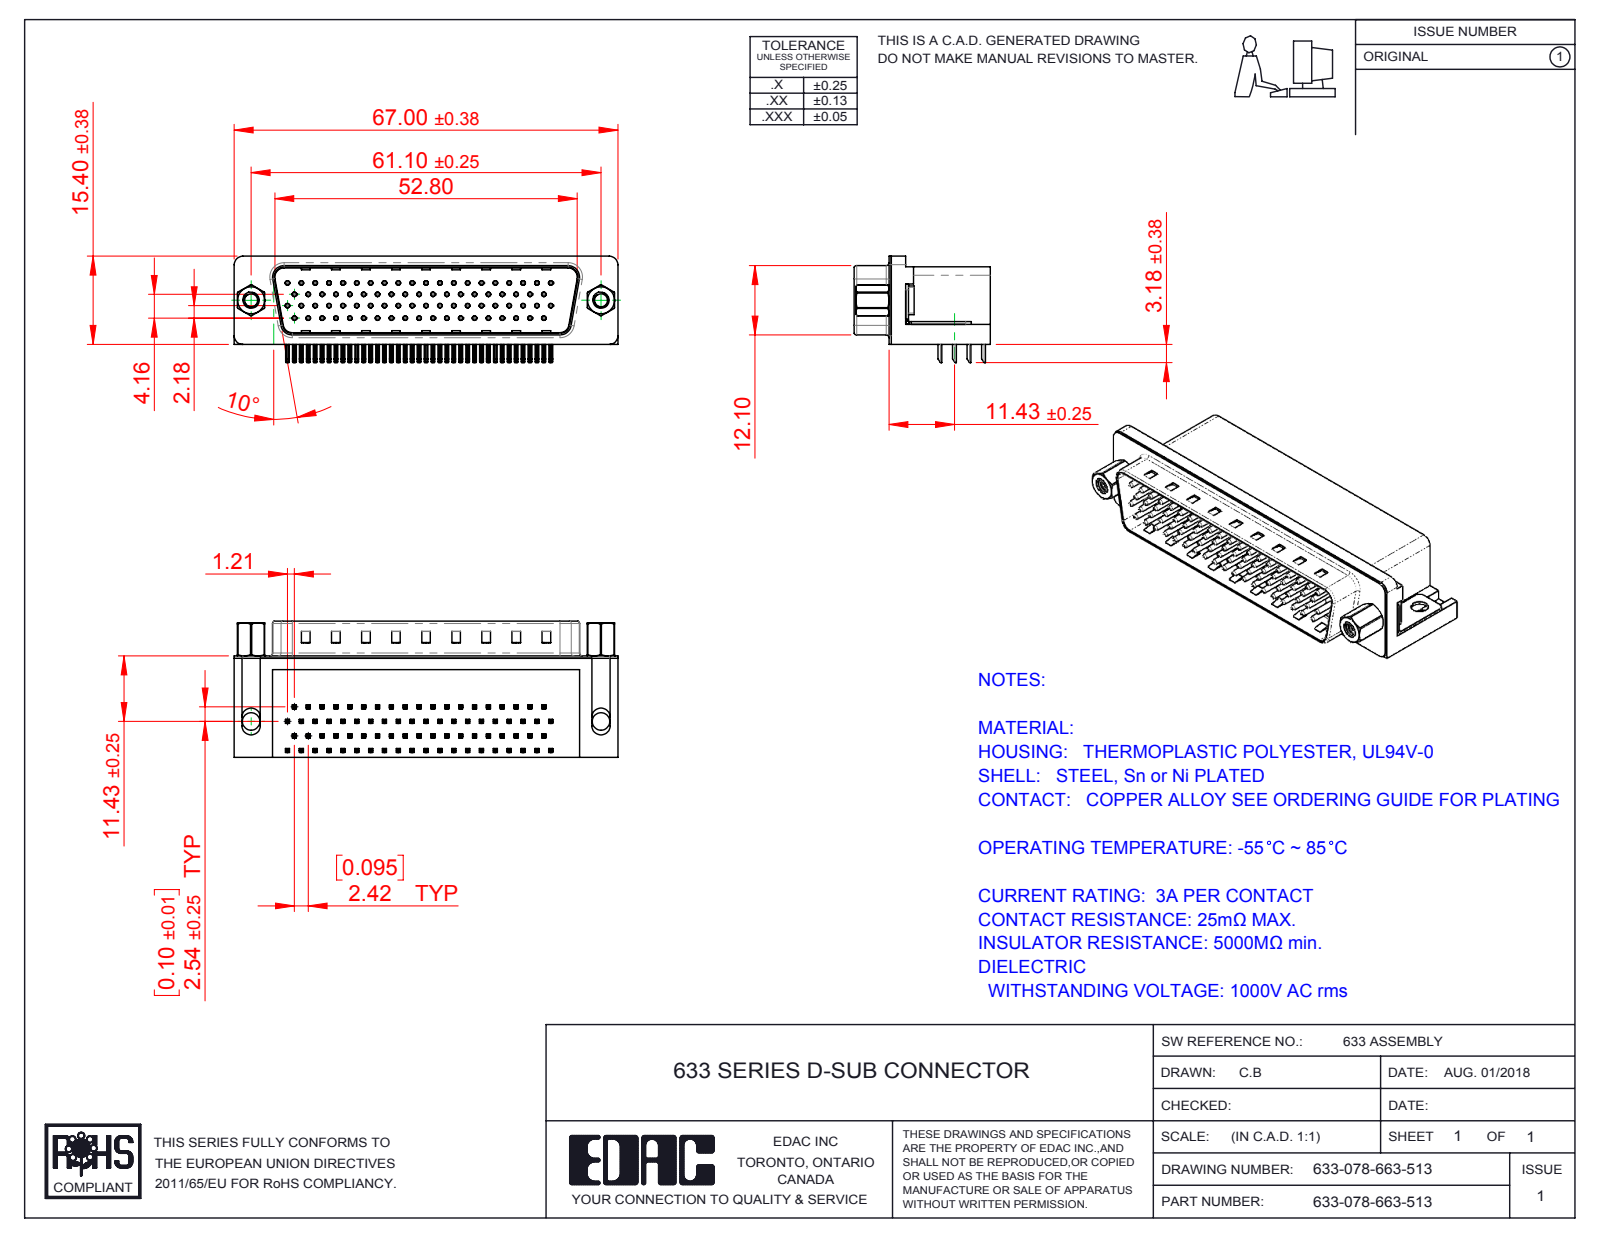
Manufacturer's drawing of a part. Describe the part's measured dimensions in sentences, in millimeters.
The part is named "633 Contact Bottom_78 Contact; 633 Contact Middle_78 Contact; 633 Shell_78 Contact; 633 Housing_78 Contact (+6 more)". Its 3-D file was written by "SolidWorks 2016 (CONFIG_CONTROL_DESIGN)". It is 86 solids with 6394 faces: 4001 planar, 1842 cylindrical and 551 other. Overall it measures 67 by 23.8 by 18.58 millimeters. Its volume is 14 813 cubic millimeters and its surface area 16 789 square millimeters. Round holes: 78 of diameter 0.35, 78 of diameter 0.8, 2 of diameter 2.26, 2 of diameter 2.29, 2 of diameter 3.05, 2 of diameter 4, 2 of diameter 4.8, 2 of diameter 5. Round bosses or shafts: 78 of diameter 0.75, 2 of diameter 4.9, 2 of diameter 4.75, 2 of diameter 3.9, 2 of diameter 2.79. Partial cylindrical surfaces (rounded edges, fillets, slot ends): 320 of radius 0.25, 156 of radius 0.12, 16 of radius 1, 9 of radius 0.5, 8 of radius 1.6, 6 of radius 1.5, 4 of radius 0.45, 4 of radius 0.9. The main face-to-face distances are 0.4, 13.2, 17.3, 11.7, 13.35, 2.05, 13.75, 1.65, 1.85, 11.9. The hole center spacings are 2.42, 4.84, 7.26, 9.68, 6.26, 7.13, 12.1, 8.62.
